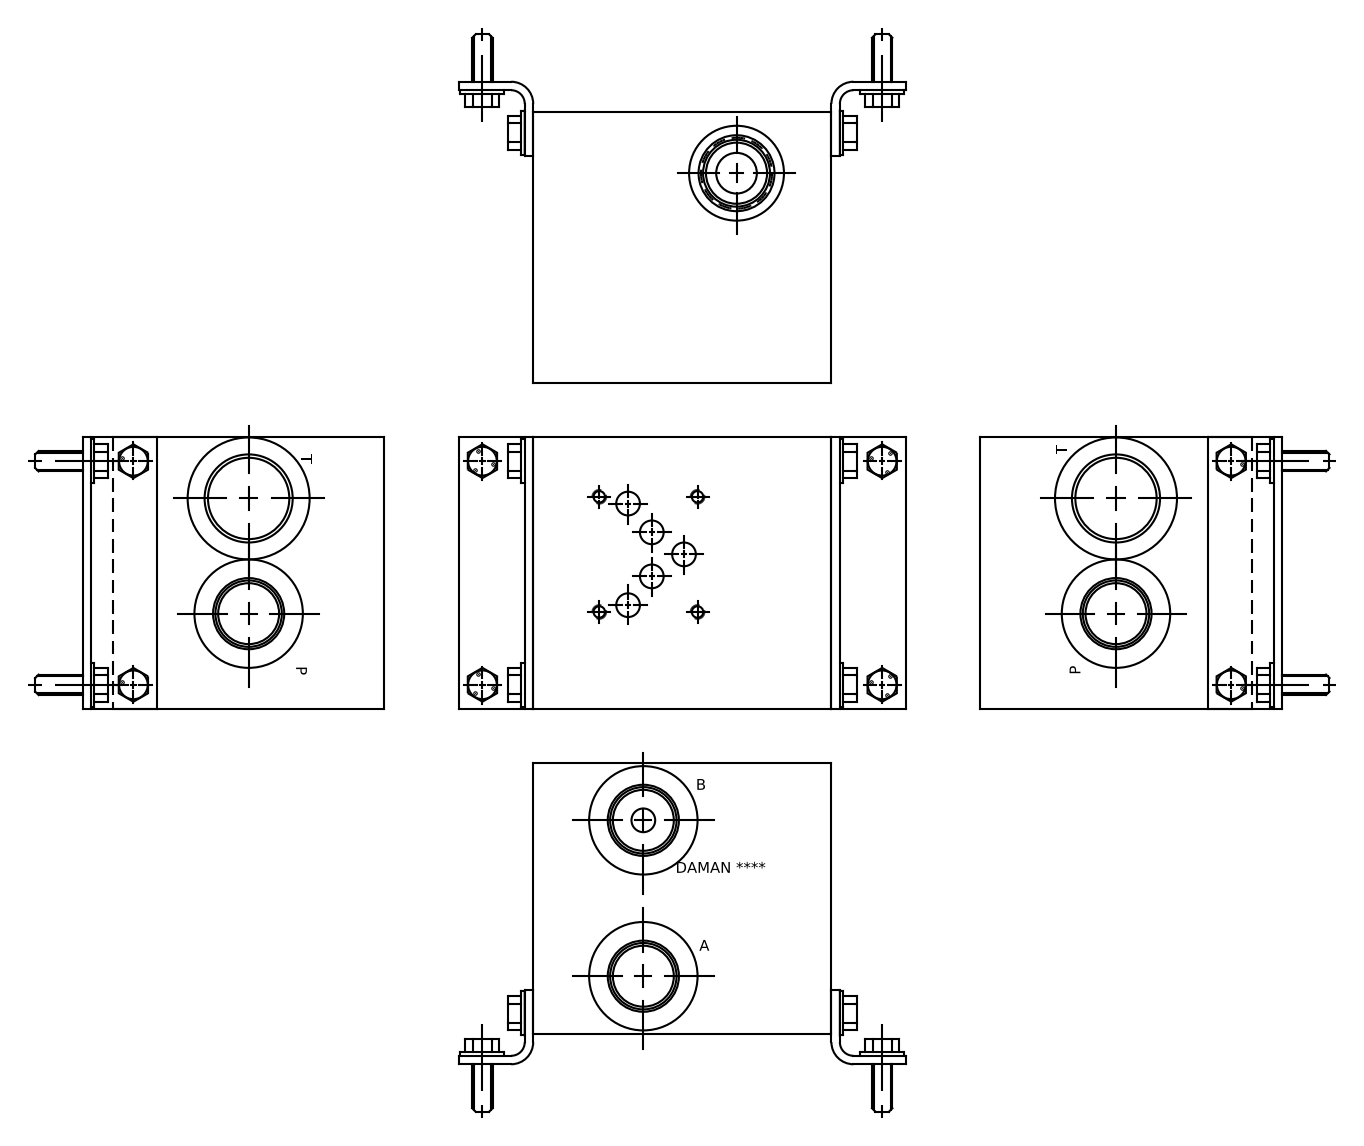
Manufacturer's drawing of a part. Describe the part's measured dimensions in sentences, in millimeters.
The part is named "Part_AD05JP013S_C_3D". Its 3-D file was written by "Autodesk Inventor 2020 (AUTOMOTIVE_DESIGN)". It is 1 solid with 569 faces: 319 planar, 58 cylindrical and 192 other. Overall it measures 139.7 by 127 by 127 millimeters. Its volume is 1 984 000 cubic millimeters and its surface area 136 781 square millimeters. Round holes: 4 of diameter 5.11, 4 of diameter 6.35, 4 of diameter 33.34, 3 of diameter 9.53, 3 of diameter 31.27, 3 of diameter 33.76, 3 of diameter 48.97, 2 of diameter 7.92, 2 of diameter 10.31, 2 of diameter 11.13, 2 of diameter 28.57, 1 of diameter 19.05. The main face-to-face distances are 127, 139.7, 0.79, 138.91, 126.21, 138.12, 19.05, 19.84, 119.86, 125.42. The hole center spacings are 17.48, 18.28, 35.4, 35.89, 13.86, 13.87, 20.64, 27.15.
